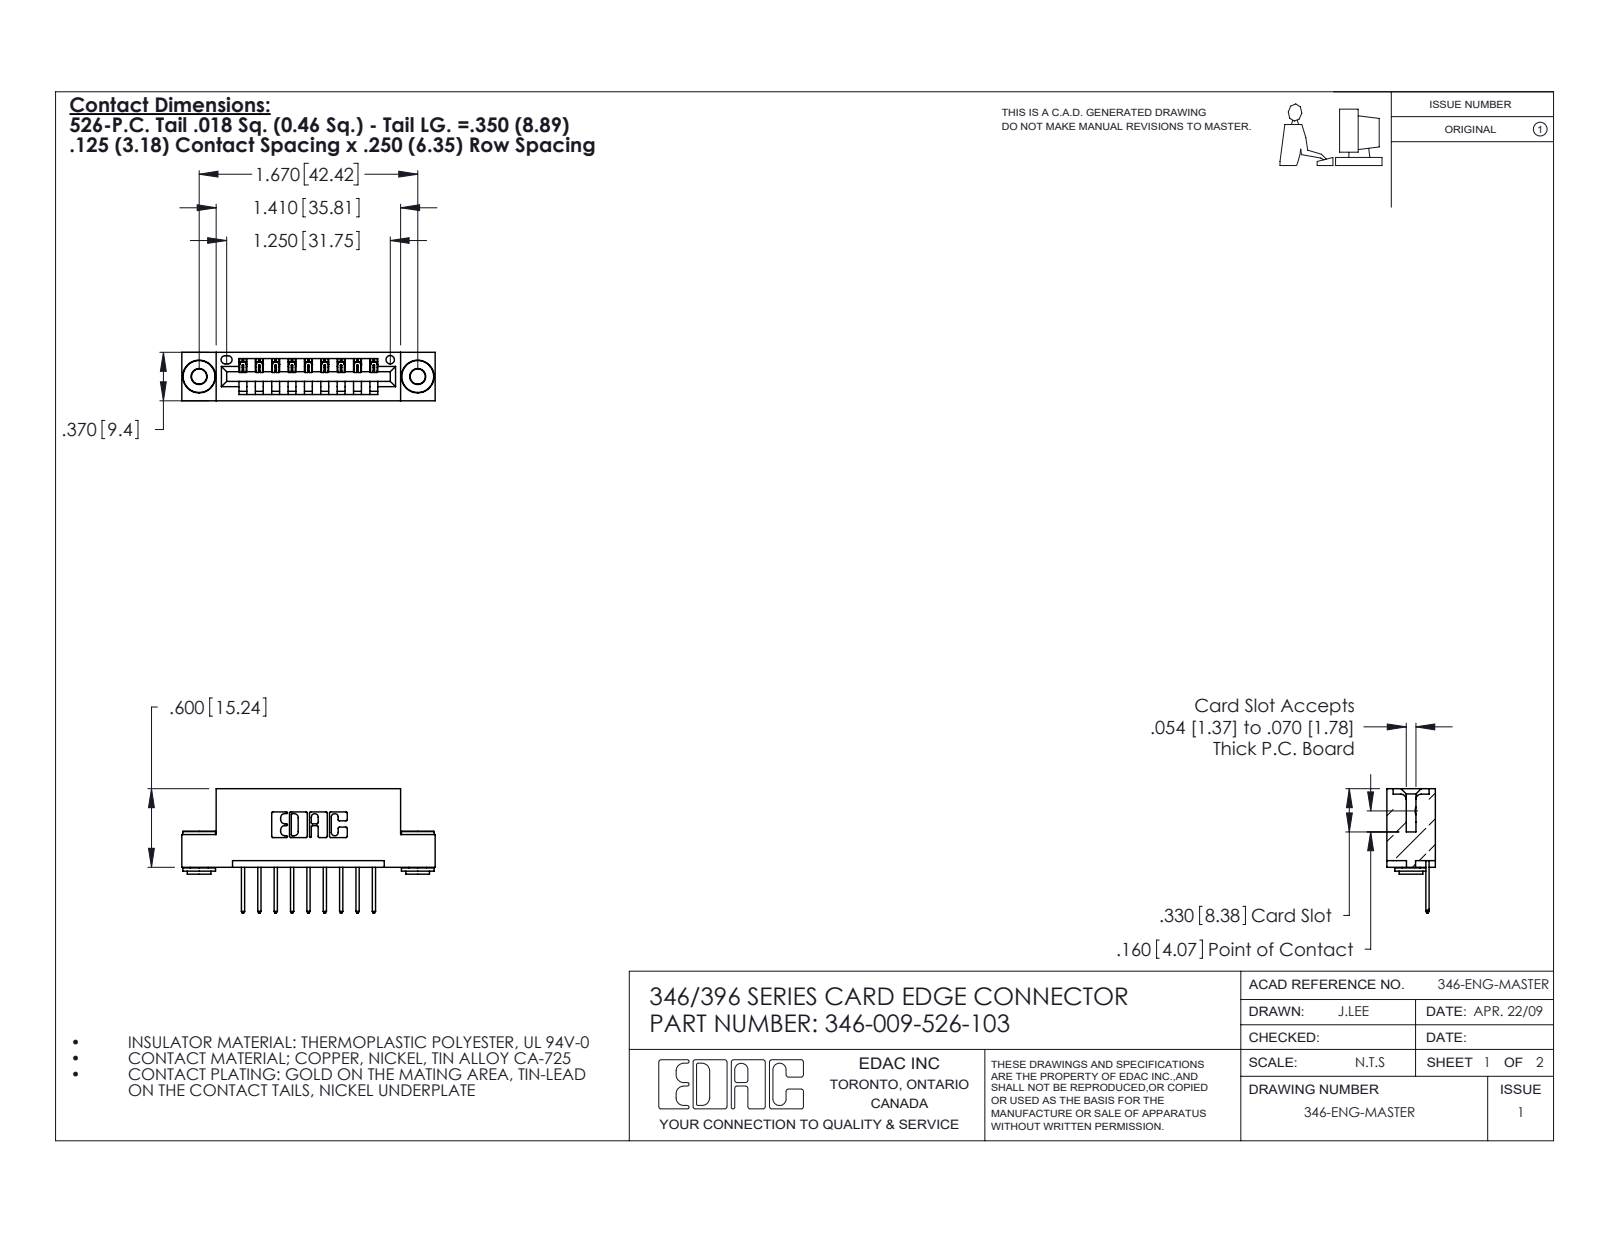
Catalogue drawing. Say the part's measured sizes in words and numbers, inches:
The part is named "345-250-002_345-250-002-102; 345-292-001_345-293-126; 346-009-526-103; 346 Part_Flush Mounting Lugs - 0.156 Dia-TH". Its 3-D file was written by "SolidWorks 2020 (CONFIG_CONTROL_DESIGN)". It is 12 solids with 696 faces: 460 planar, 228 cylindrical and 8 other. Overall it measures 1.935 by 0.95 by 0.37 inches. Its volume is 0.273 cubic inches and its surface area 8.487 square inches. Round holes: 2 of diameter 0.116, 2 of diameter 0.156, 1 of diameter 0.064. Round bosses or shafts: 2 of diameter 0.25, 2 of diameter 0.18, 2 of diameter 0.136. Partial cylindrical surfaces (rounded edges, fillets, slot ends): 22 of radius 0.01, 18 of radius 0.006, 18 of radius 0.01, 6 of radius 0.007, 6 of radius 0.031, 3 of radius 0.026, 2 of radius 0.031, 2 of radius 0.04. The main face-to-face distances are 0.25, 0.37, 0.048, 0.322, 0.025, 0.072, 0.298, 0.148, 0.222, 0.1. The hole center spacings are 0.246, 1.465, 1.67.
